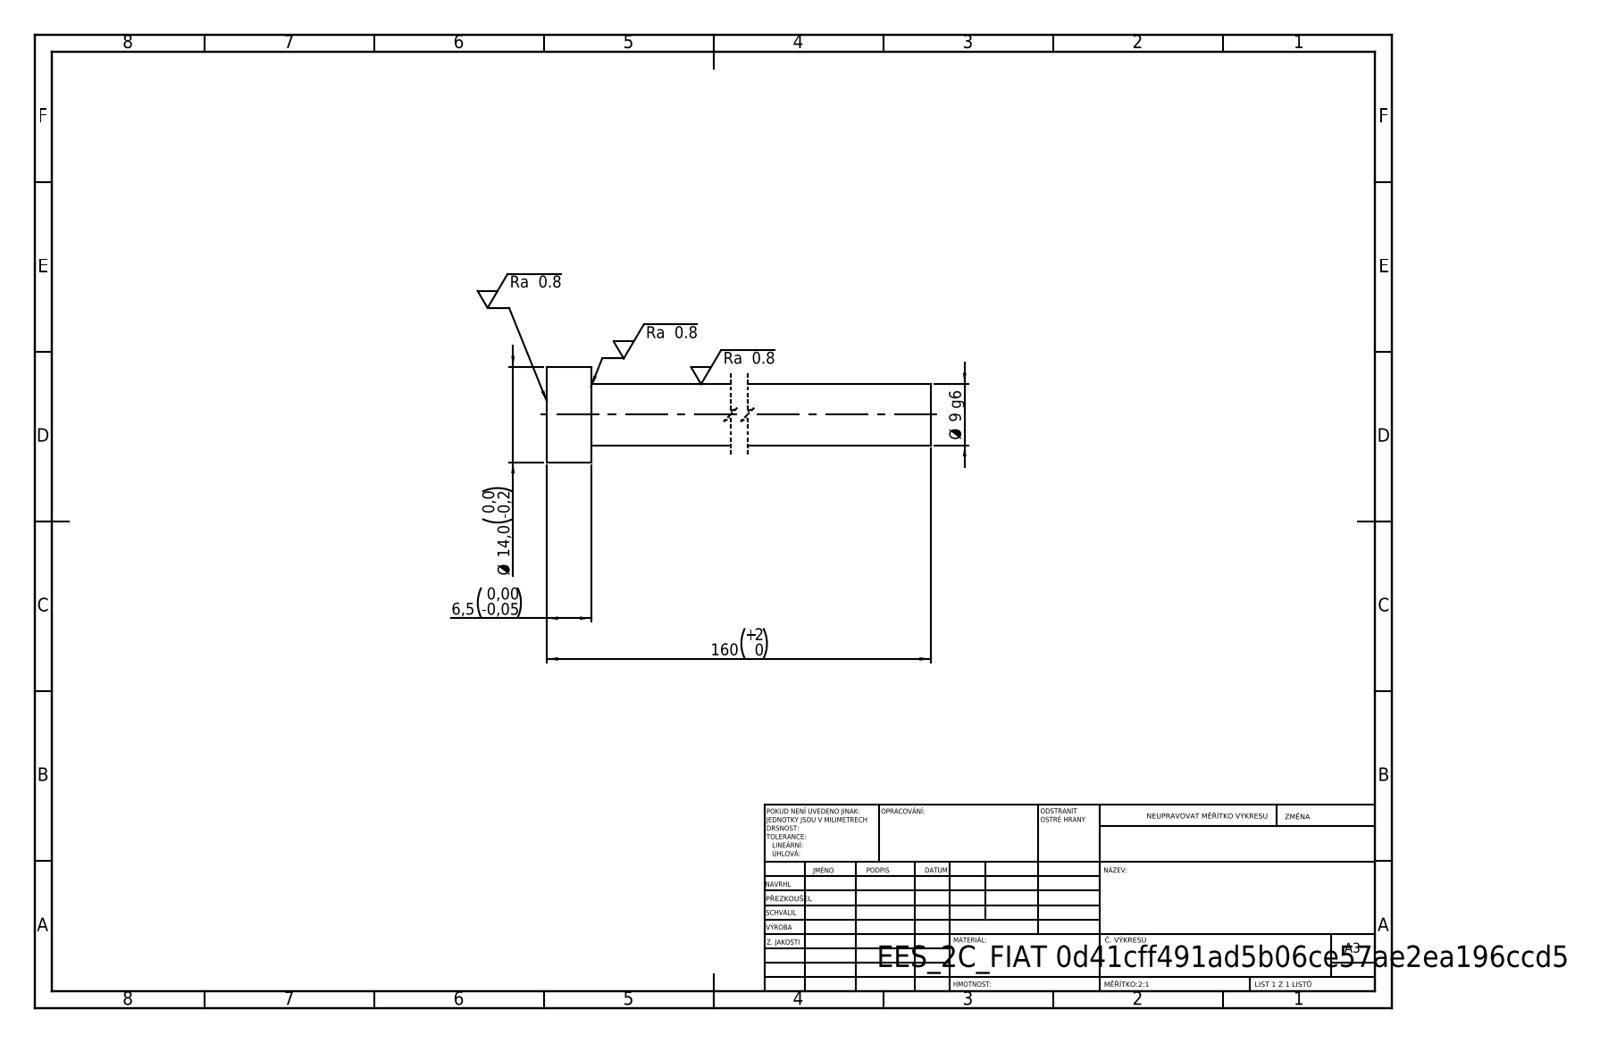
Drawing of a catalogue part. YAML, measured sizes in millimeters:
step_written_by: "SolidWorks 2019 (CONFIG_CONTROL_DESIGN)"
units: millimeters
bodies: {solids: 1, faces: 7, planar: 3, cylindrical: 4, other: 0}
overall_size: [160, 14, 14]
volume: 10766
surface_area: 4934
round_bosses_or_shafts:
  - {diameter: 14, count: 1}
  - {diameter: 9, count: 1}
face_to_face_distances: [6.5, 160, 153.5]
